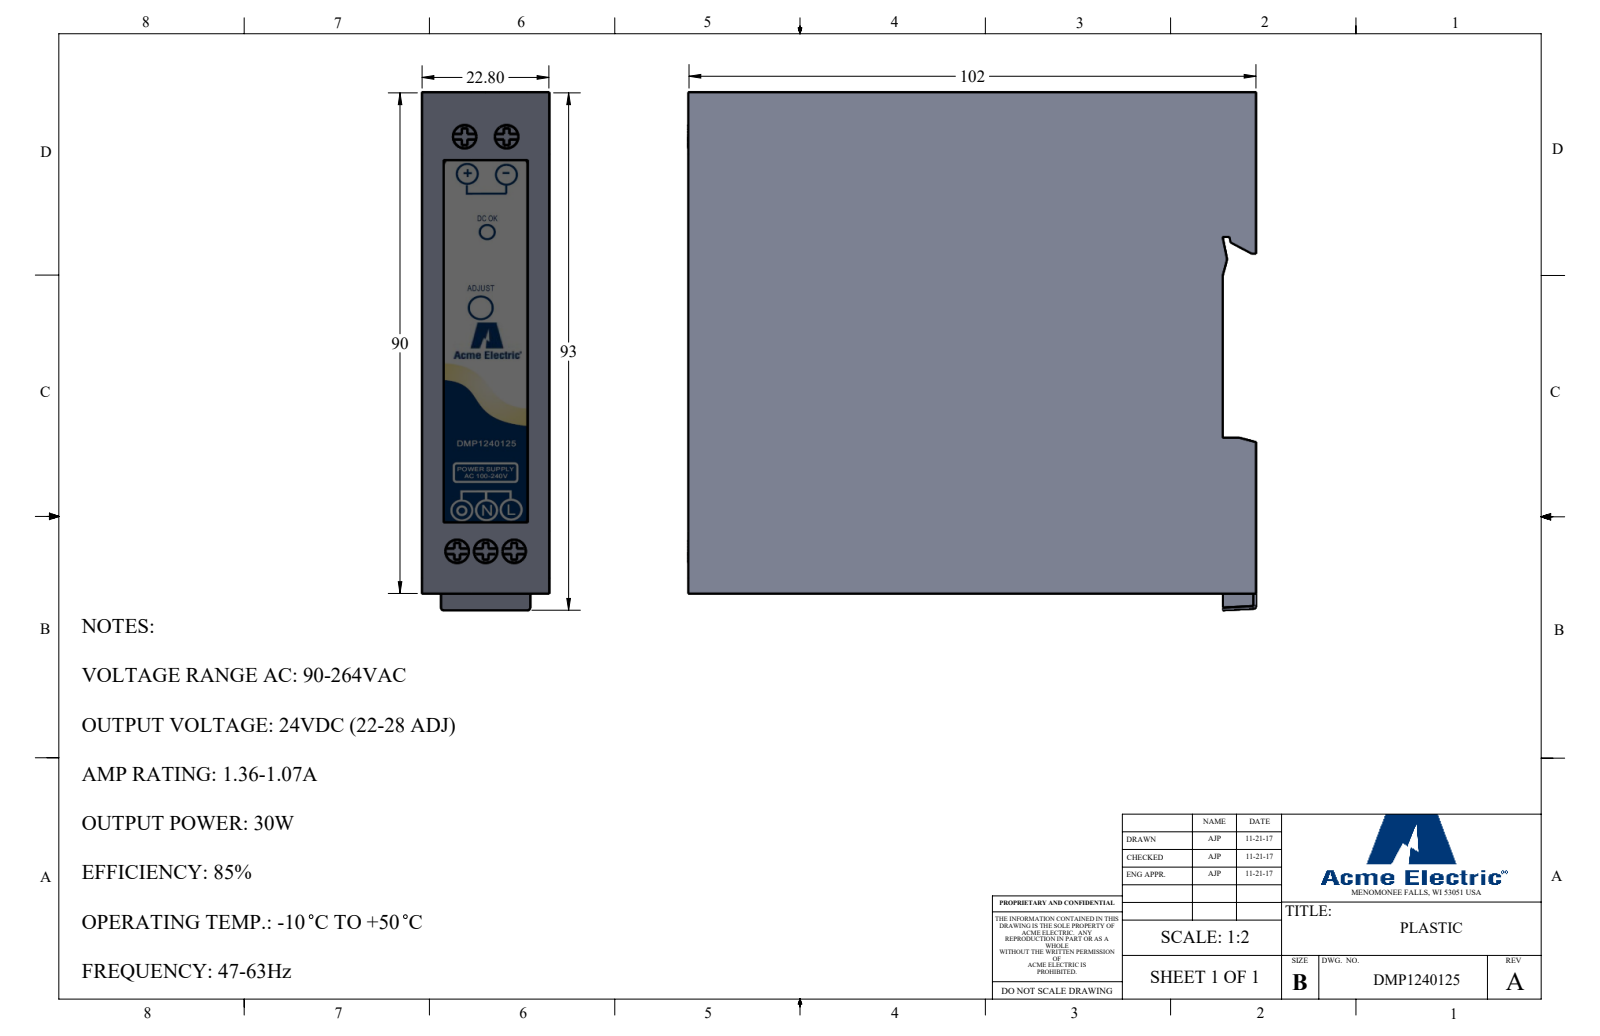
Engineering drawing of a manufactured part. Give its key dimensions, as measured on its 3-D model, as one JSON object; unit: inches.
{"part_name": "DMP1240125", "step_written_by": "SolidWorks 2017 (AUTOMOTIVE_DESIGN)", "units": "inches", "bodies": {"solids": 1, "faces": 103, "planar": 86, "cylindrical": 15, "other": 2}, "overall_size": [4.016, 3.661, 0.898], "volume_in3": 12.5, "surface_area_in2": 42.27, "round_holes": [[0.165, 5]], "partial_cylinders_radius": [[0.02, 5]], "face_to_face_distances": [0.898, 3.543, 4.016, 0.236, 3.78, 1.102, 2.441, 0.039, 3.976, 3.74], "hole_center_spacings": [0.201, 2.93, 2.933, 2.95, 0.295, 0.402]}
